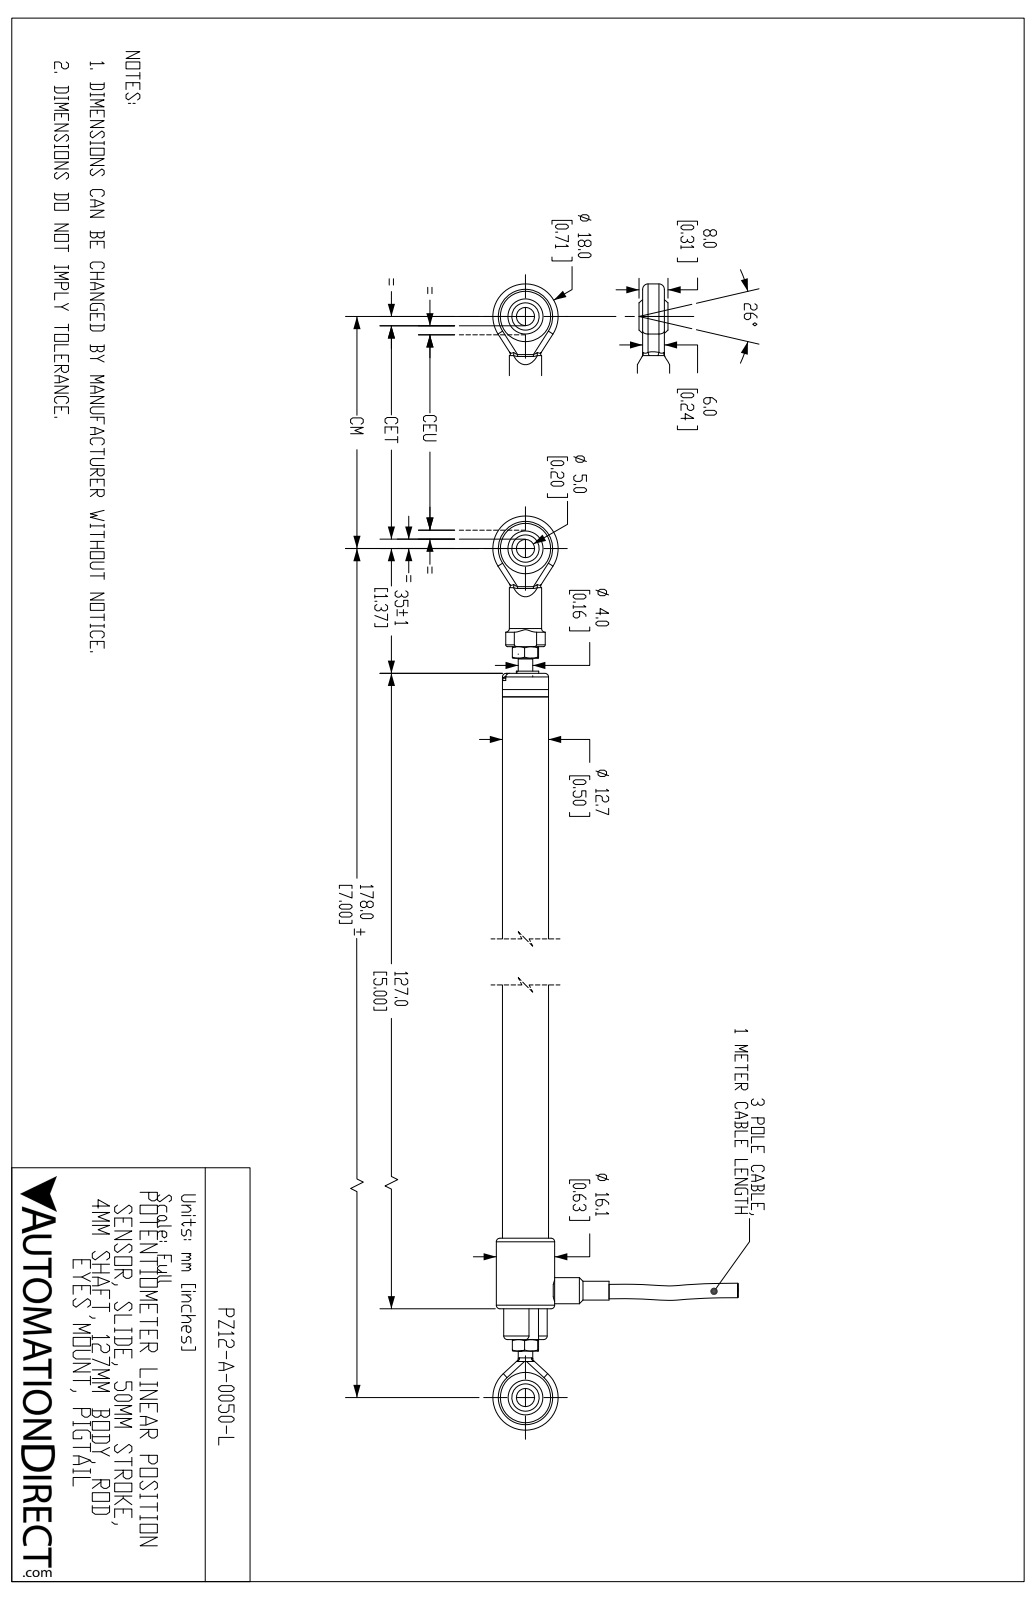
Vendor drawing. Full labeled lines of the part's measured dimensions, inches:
Part name (STEP PRODUCT): PZ12-A-0050-L
STEP written by: SolidWorks 2019 (AUTOMOTIVE_DESIGN)
Units: inches
Bodies: 18 solids, 648 faces (168 planar, 170 cylindrical, 310 other)
Overall size (bounding box): 7.695 × 2.671 × 0.634
Volume: 1.514 in³ · Surface area: 23.49 in²
Round holes (diameter × count): ⌀0.138 ×3, ⌀0.039 ×2, ⌀0.055 ×2, ⌀0.079 ×2, ⌀0.197 ×2, ⌀0.547 ×2, ⌀0.126 ×1, ⌀0.13 ×1, ⌀0.201 ×1, ⌀0.508 ×1
Round bosses / shafts (diameter × count): ⌀0.126 ×4, ⌀0.063 ×4, ⌀0.634 ×1, ⌀0.5 ×1, ⌀0.472 ×1, ⌀0.35 ×1, ⌀0.283 ×1, ⌀0.236 ×1
Partial cylindrical surfaces — rounded edges, fillets, slot ends (radius × count): R0.059 ×8, R0.01 ×4, R0.02 ×2, R0.039 ×2, R0.069 ×2, R0.354 ×2, R0.017 ×1, R0.103 ×1
Main face-to-face distances: 0.079, 4.035, 4.114, 0.276, 0.224, 0.213, 0.236, 0.177, 5.289, 0.039
Hole centre spacings: 0.189, 0.096, 0.167, 0.189, 0.248, 0.285, 0.339, 0.365
